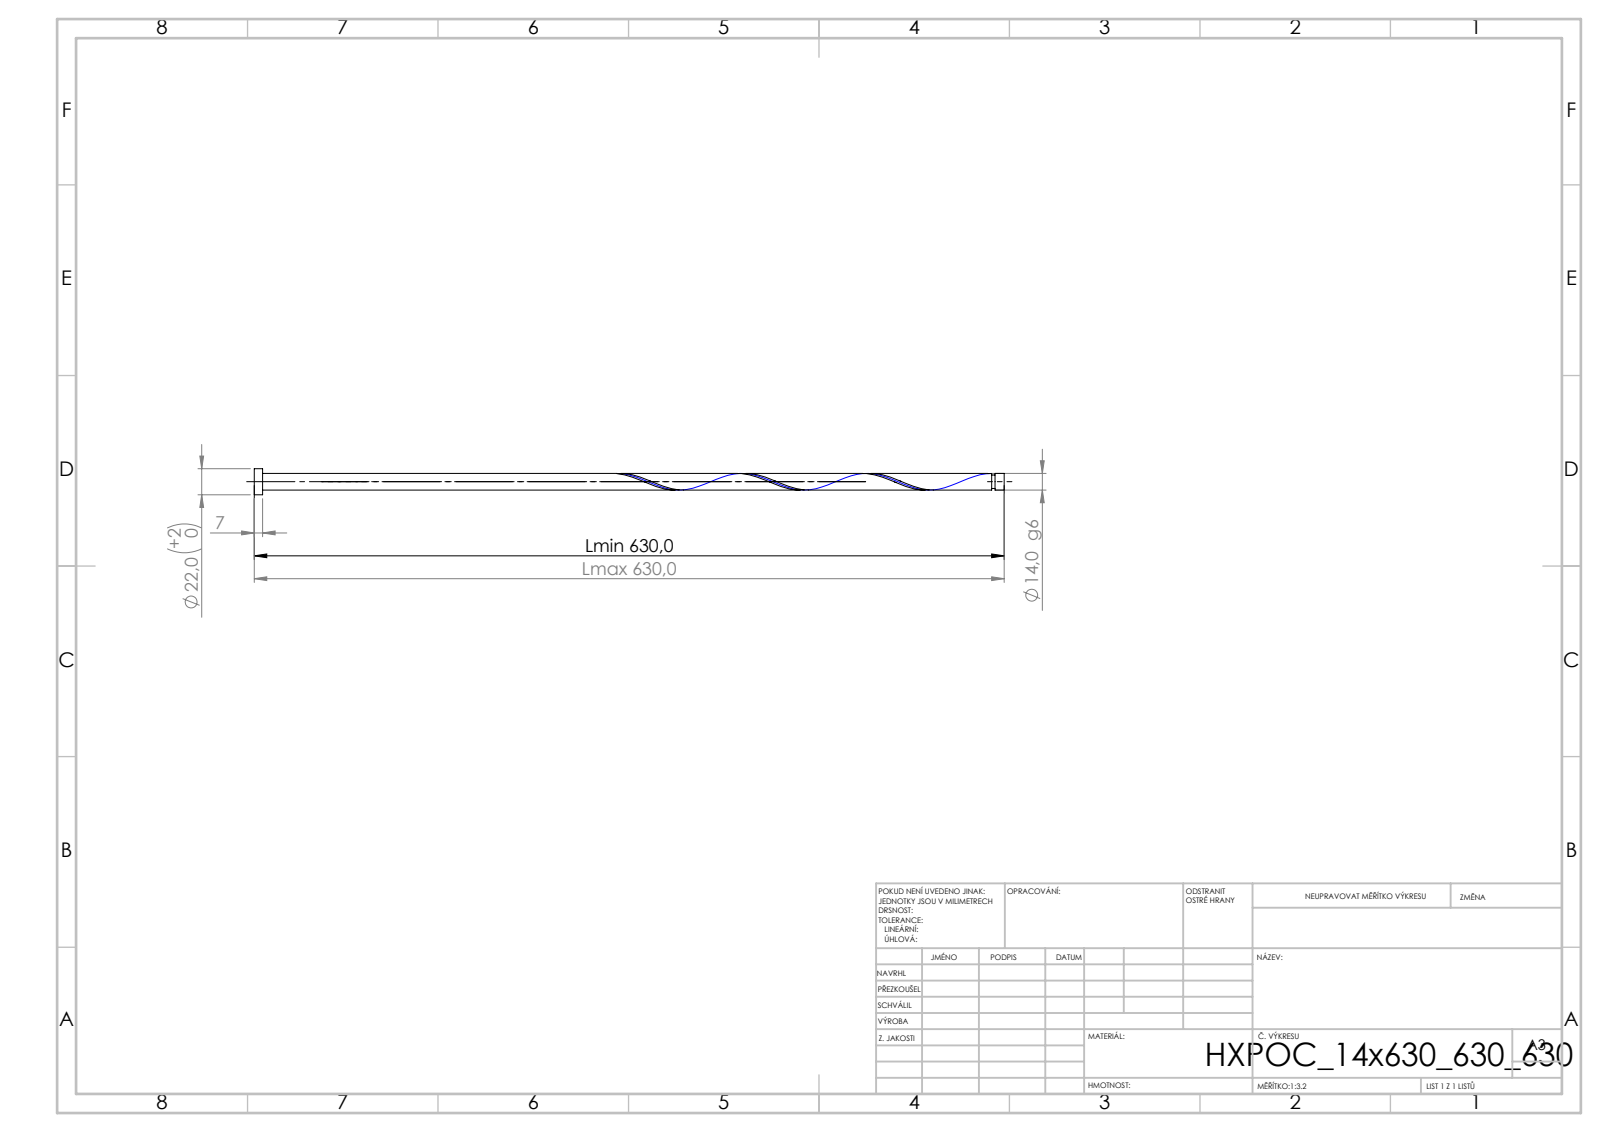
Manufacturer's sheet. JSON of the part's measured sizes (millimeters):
{"step_written_by": "SolidWorks 2019 (CONFIG_CONTROL_DESIGN)", "units": "millimeters", "bodies": {"solids": 1, "faces": 21, "planar": 6, "cylindrical": 14, "other": 1}, "overall_size": [630, 22, 22], "volume_mm3": 97481, "surface_area_mm2": 29196, "round_bosses_or_shafts": [[22, 1], [14, 1], [11.2, 1]], "face_to_face_distances": [7, 630, 623, 622.3, 615.3, 7.7, 619.5, 612.5, 2.8, 10.5]}
